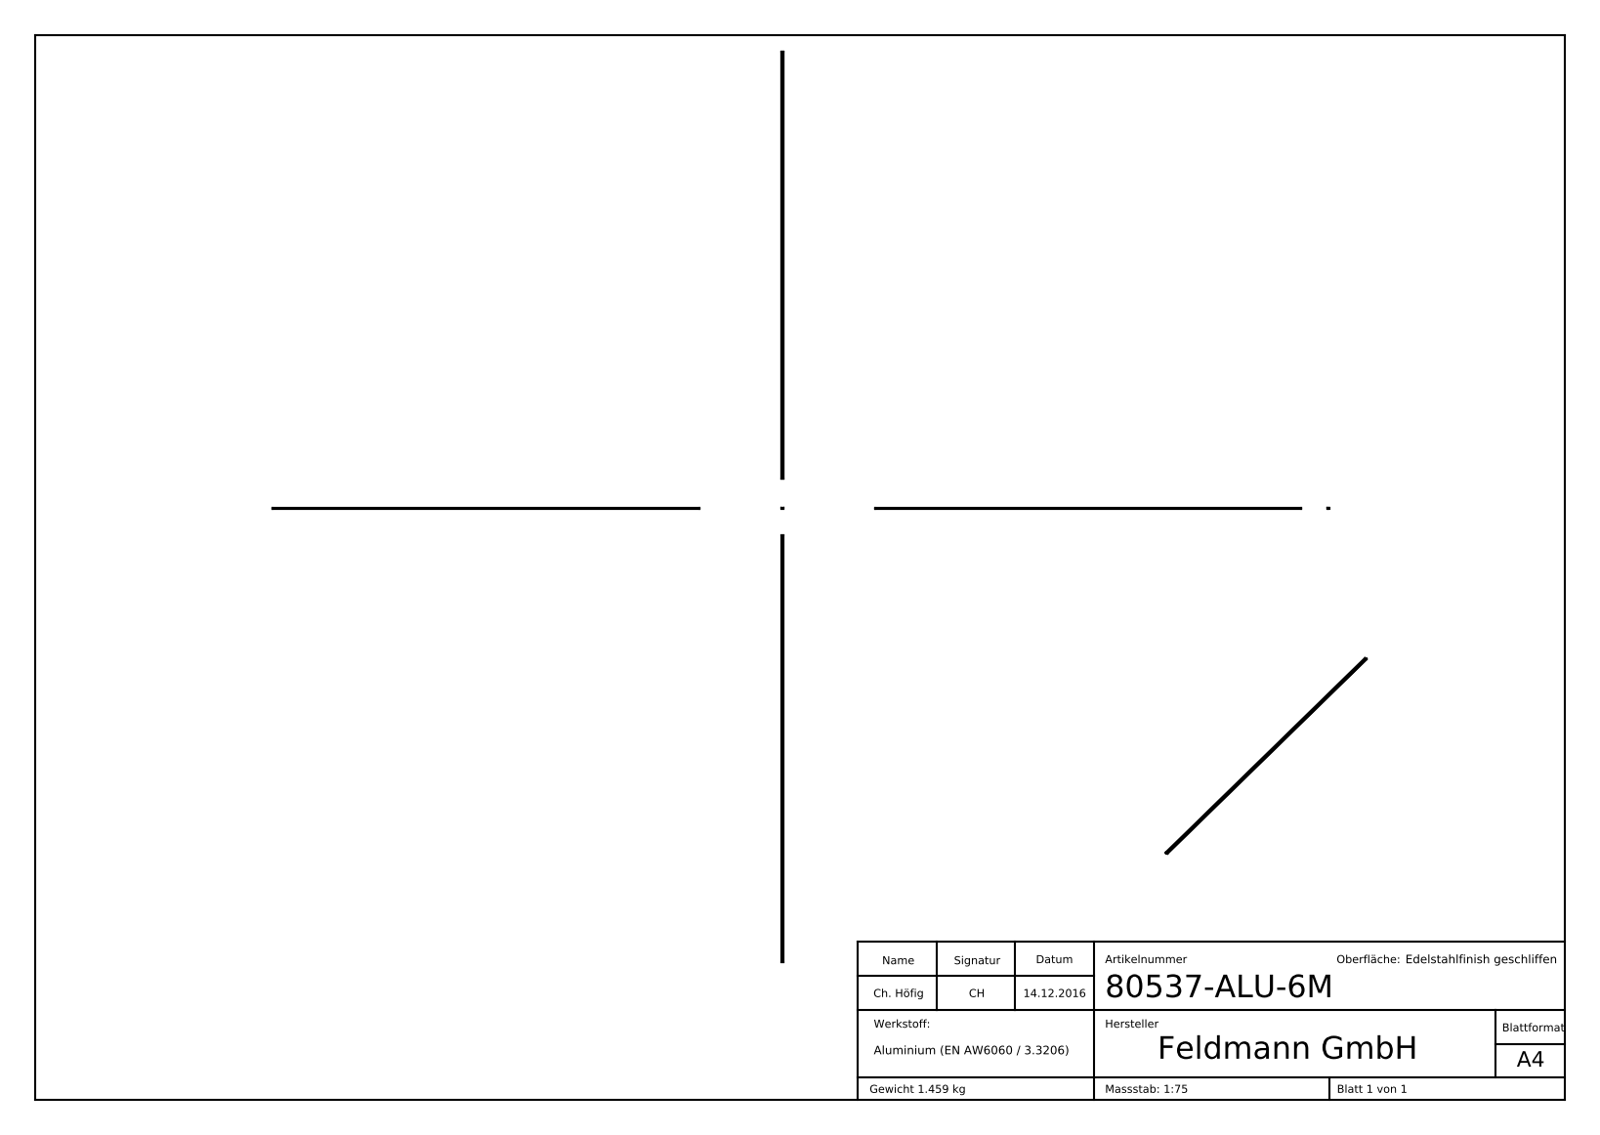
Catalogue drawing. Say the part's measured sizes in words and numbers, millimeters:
The part is named "80537-ALU-6M". Its 3-D file was written by "SolidWorks 2015 (CONFIG_CONTROL_DESIGN)". It is 1 solid with 304 faces: 172 planar, 6 cylindrical and 126 other. Overall it measures 6000 by 26 by 12 millimeters. Its volume is 540 411 cubic millimeters and its surface area 560 745 square millimeters. Partial cylindrical surfaces (rounded edges, fillets, slot ends): 4 of radius 0.5, 2 of radius 2. The main face-to-face distances are 2, 24, 26, 22, 10, 12, 6000, 1.9, 22.1, 24.1.
